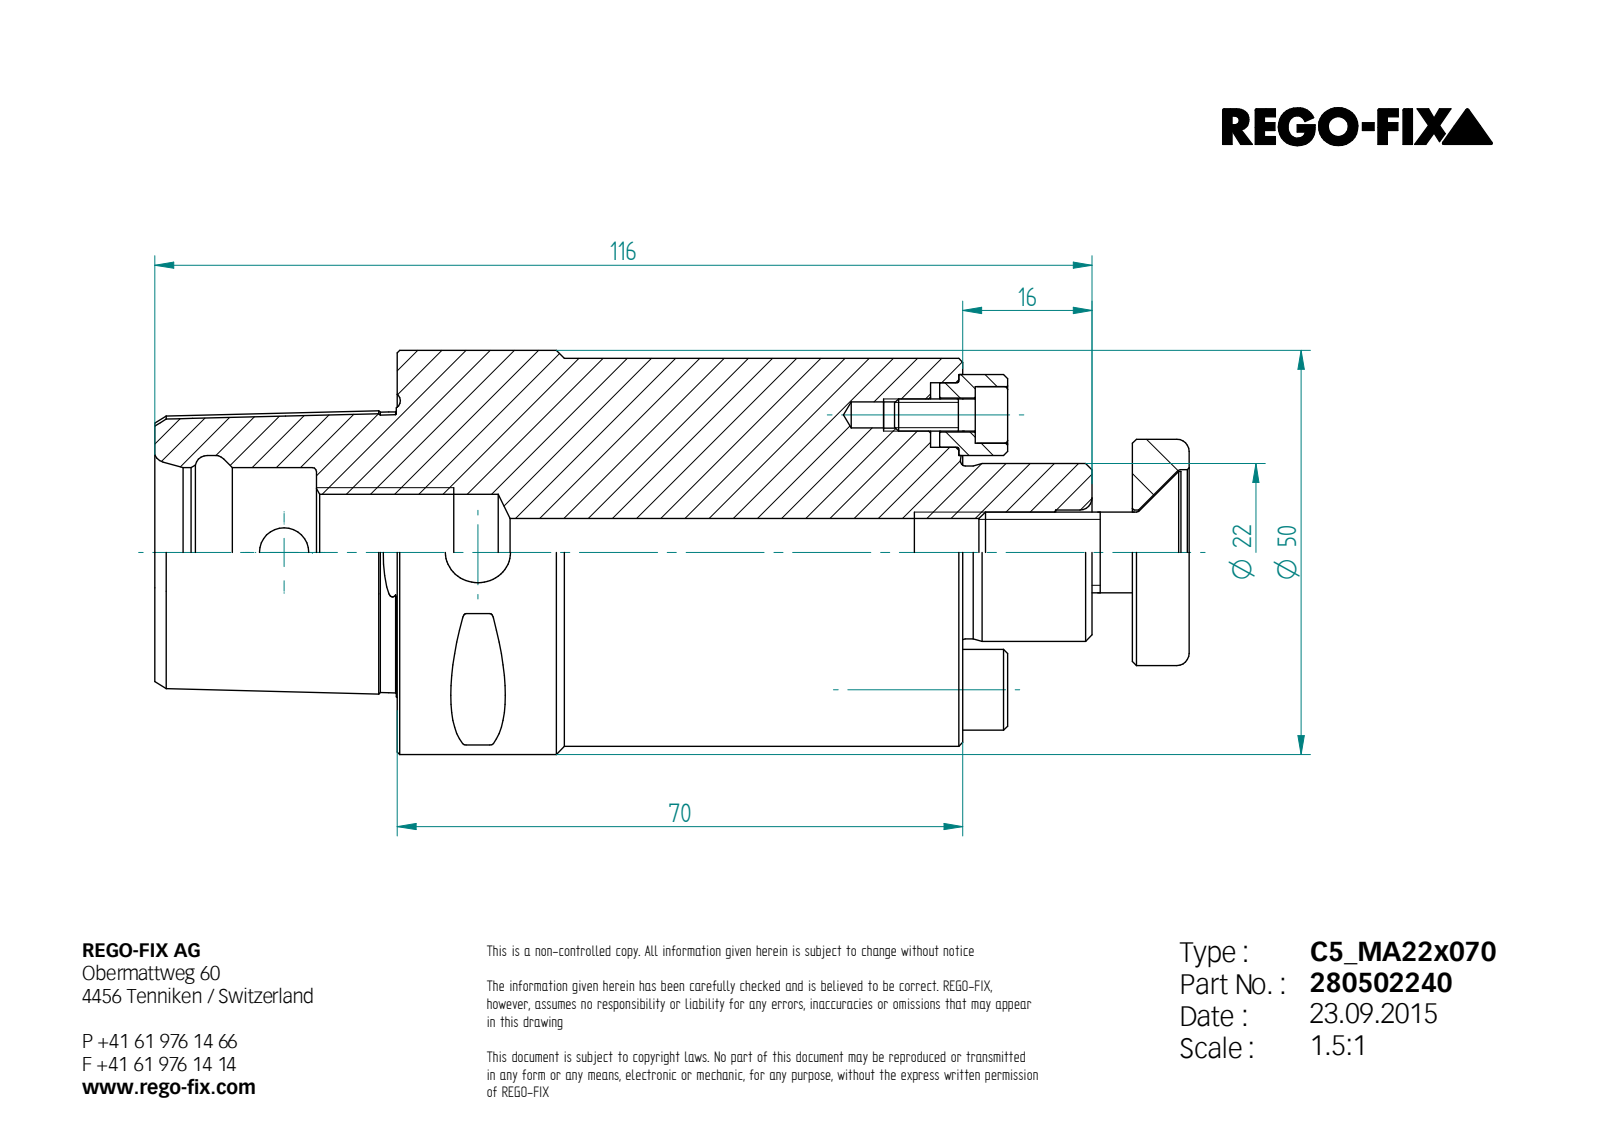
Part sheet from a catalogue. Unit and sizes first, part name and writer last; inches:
Units: inches
Overall size (bounding box): 5.039 × 1.969 × 1.969
Round holes (diameter × count): ⌀0.127 ×2, ⌀0.128 ×2, ⌀0.165 ×2, ⌀0.315 ×2, ⌀0.394 ×2, ⌀0.157 ×1, ⌀0.24 ×1, ⌀0.33 ×1, ⌀0.413 ×1, ⌀0.566 ×1, ⌀0.807 ×1, ⌀0.827 ×1
Round bosses / shafts (diameter × count): ⌀0.276 ×2, ⌀0.157 ×2, ⌀1.969 ×1, ⌀1.89 ×1, ⌀1.102 ×1, ⌀0.866 ×1, ⌀0.843 ×1, ⌀0.787 ×1
Partial cylindrical surfaces — rounded edges, fillets, slot ends (radius × count): R0.02 ×8, R0.157 ×1
Main face-to-face distances: 2.756, 0.827, 3.583, 0.236, 1.181, 3.937, 4.764, 3.819, 5, 1.063
Hole centre spacings: 0.669, 1.024, 1.339
Volume: 9.285 in³ · Surface area: 44.12 in²
Bodies: 7 solids, 241 faces (67 planar, 65 cylindrical, 109 other)
Part name (STEP PRODUCT): 0003451; 0003387; 0010452; 0010451 (+1 more)
STEP written by: Unknown (AUTOMOTIVE_DESIGN)
